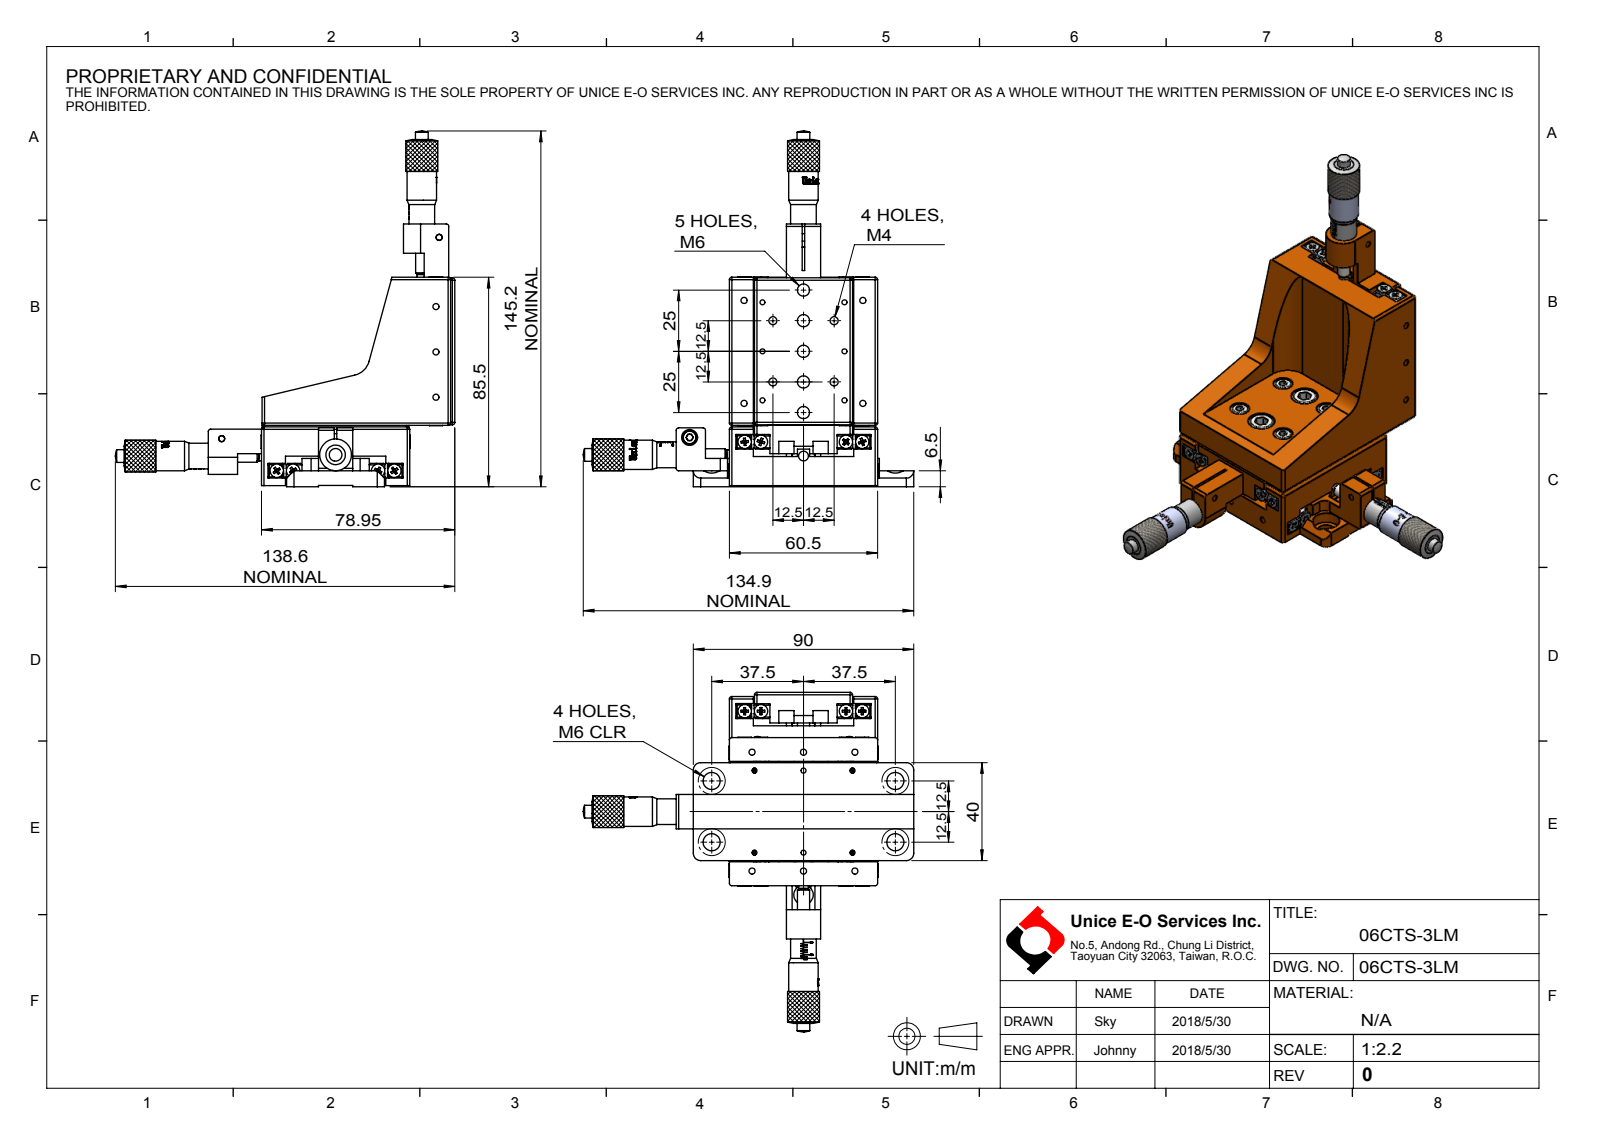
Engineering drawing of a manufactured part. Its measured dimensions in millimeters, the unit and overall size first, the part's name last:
Units: millimetres
Overall size (bounding box): 145.15 × 138.6 × 134.9
Round holes (diameter × count): ⌀2.5 ×22, ⌀2.05 ×14, ⌀8 ×6, ⌀11 ×6, ⌀5 ×5, ⌀3.3 ×4, ⌀7 ×4, ⌀6.5 ×3, ⌀9.5 ×3, ⌀1.6 ×2, ⌀4 ×1
Round bosses / shafts (diameter × count): ⌀5.5 ×15, ⌀7 ×4, ⌀13 ×3, ⌀12 ×3, ⌀10.5 ×3, ⌀5.2 ×3, ⌀5 ×3, ⌀10 ×2
Partial cylindrical surfaces — rounded edges, fillets, slot ends (radius × count): R1 ×38, R3 ×6, R1.5 ×3, R5.98 ×3, R2 ×2, R7 ×2, R8.5 ×2, R8 ×1
Main face-to-face distances: 3, 6, 9, 16.5, 60.5, 12.5, 3.1, 12, 11.8, 6.75
Hole centre spacings: 25, 12.5, 8.62, 13.2, 17.68, 20, 27.95, 30.2
Bodies: 0 solids, 1281 faces (788 planar, 346 cylindrical, 147 other)
Part name (STEP PRODUCT): 06CTS-3LM
STEP written by: SolidWorks 2016 (AUTOMOTIVE_DESIGN)
